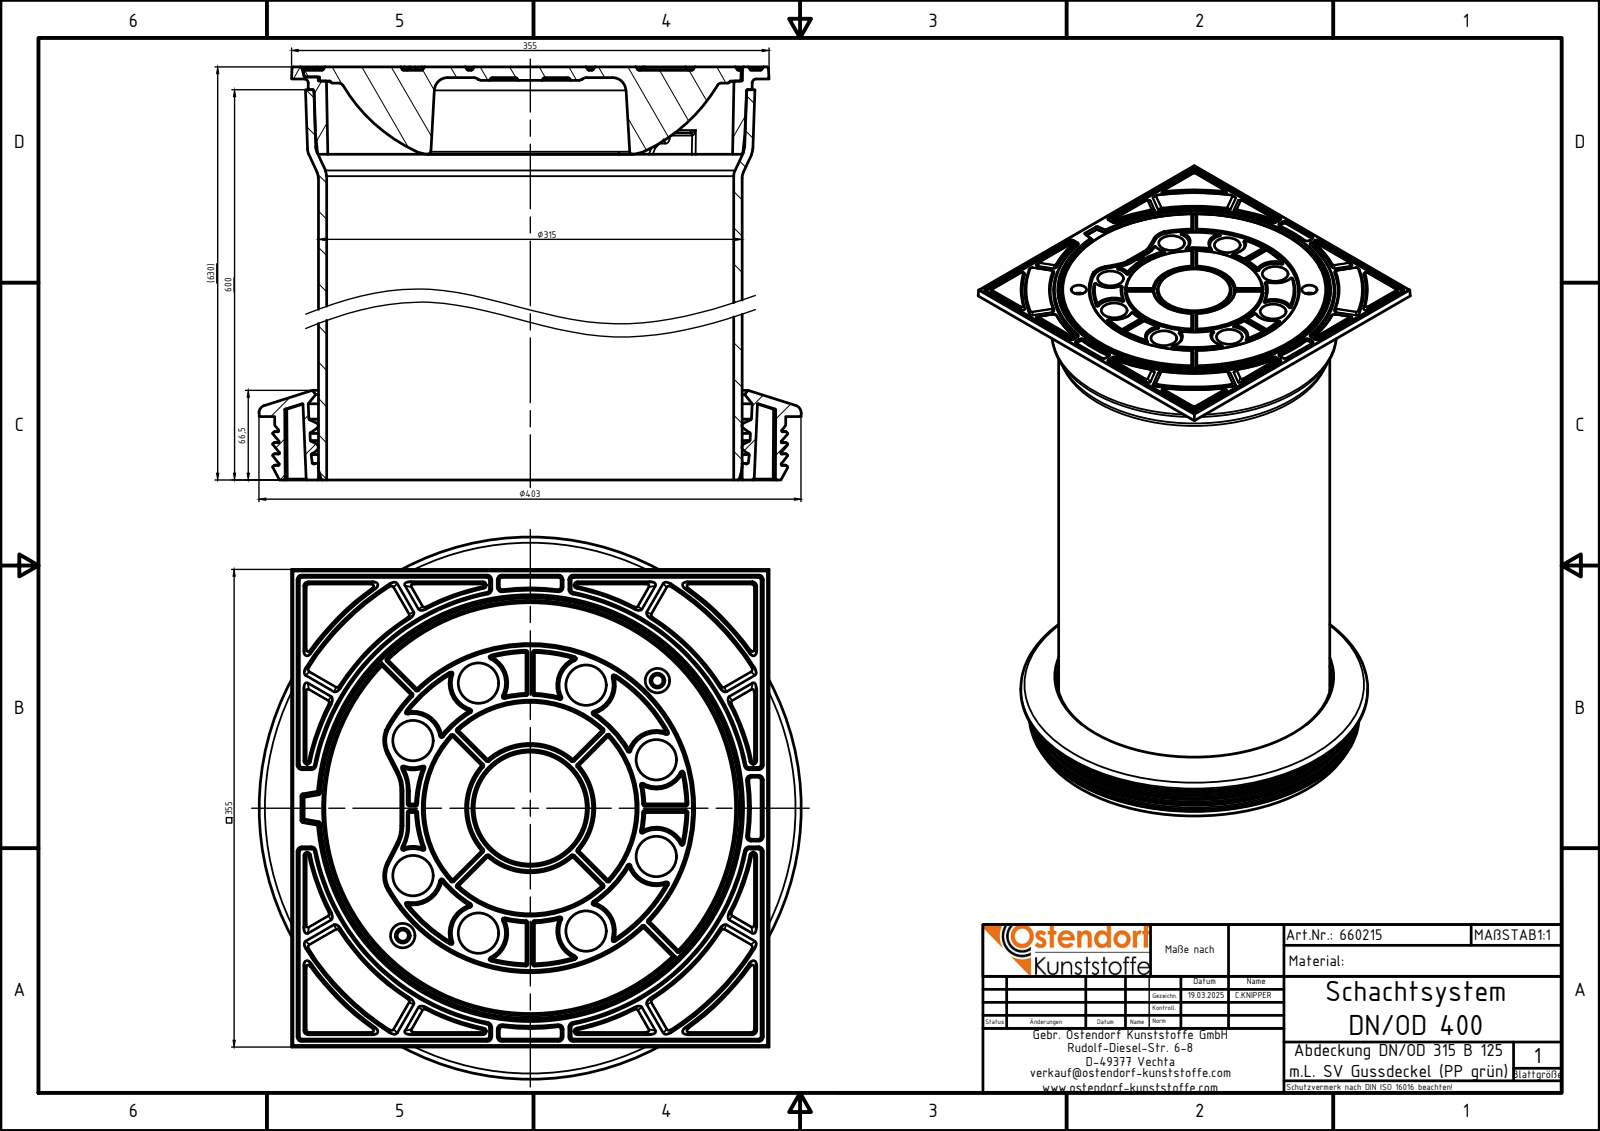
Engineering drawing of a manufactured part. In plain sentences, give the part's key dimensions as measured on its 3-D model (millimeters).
The part is named "660215z; 660205_Dichtungz; 660205_geändertz; 990000z (+2 more)". Its 3-D file was written by "Autodesk Inventor 2024 (AUTOMOTIVE_DESIGN)". It is 4 solids with 1528 faces: 200 planar, 257 cylindrical and 1071 other. Overall it measures 617 by 403 by 403 millimeters. Its volume is 7 841 000 cubic millimeters and its surface area 2 067 000 square millimeters. Round holes: 8 of diameter 30, 2 of diameter 8.38, 2 of diameter 11, 2 of diameter 18, 1 of diameter 302.6, 1 of diameter 315. Round bosses or shafts: 1 of diameter 403, 1 of diameter 380, 1 of diameter 330. Partial cylindrical surfaces (rounded edges, fillets, slot ends): 161 of radius 1, 8 of radius 2, 8 of radius 2.5. The main face-to-face distances are 9, 8, 2.5, 6.5, 608, 614.5, 617, 1.5, 47, 561. The hole center spacings are 100.5, 64.61, 76.11, 80.14, 134, 135.14, 143.97, 151.12.
